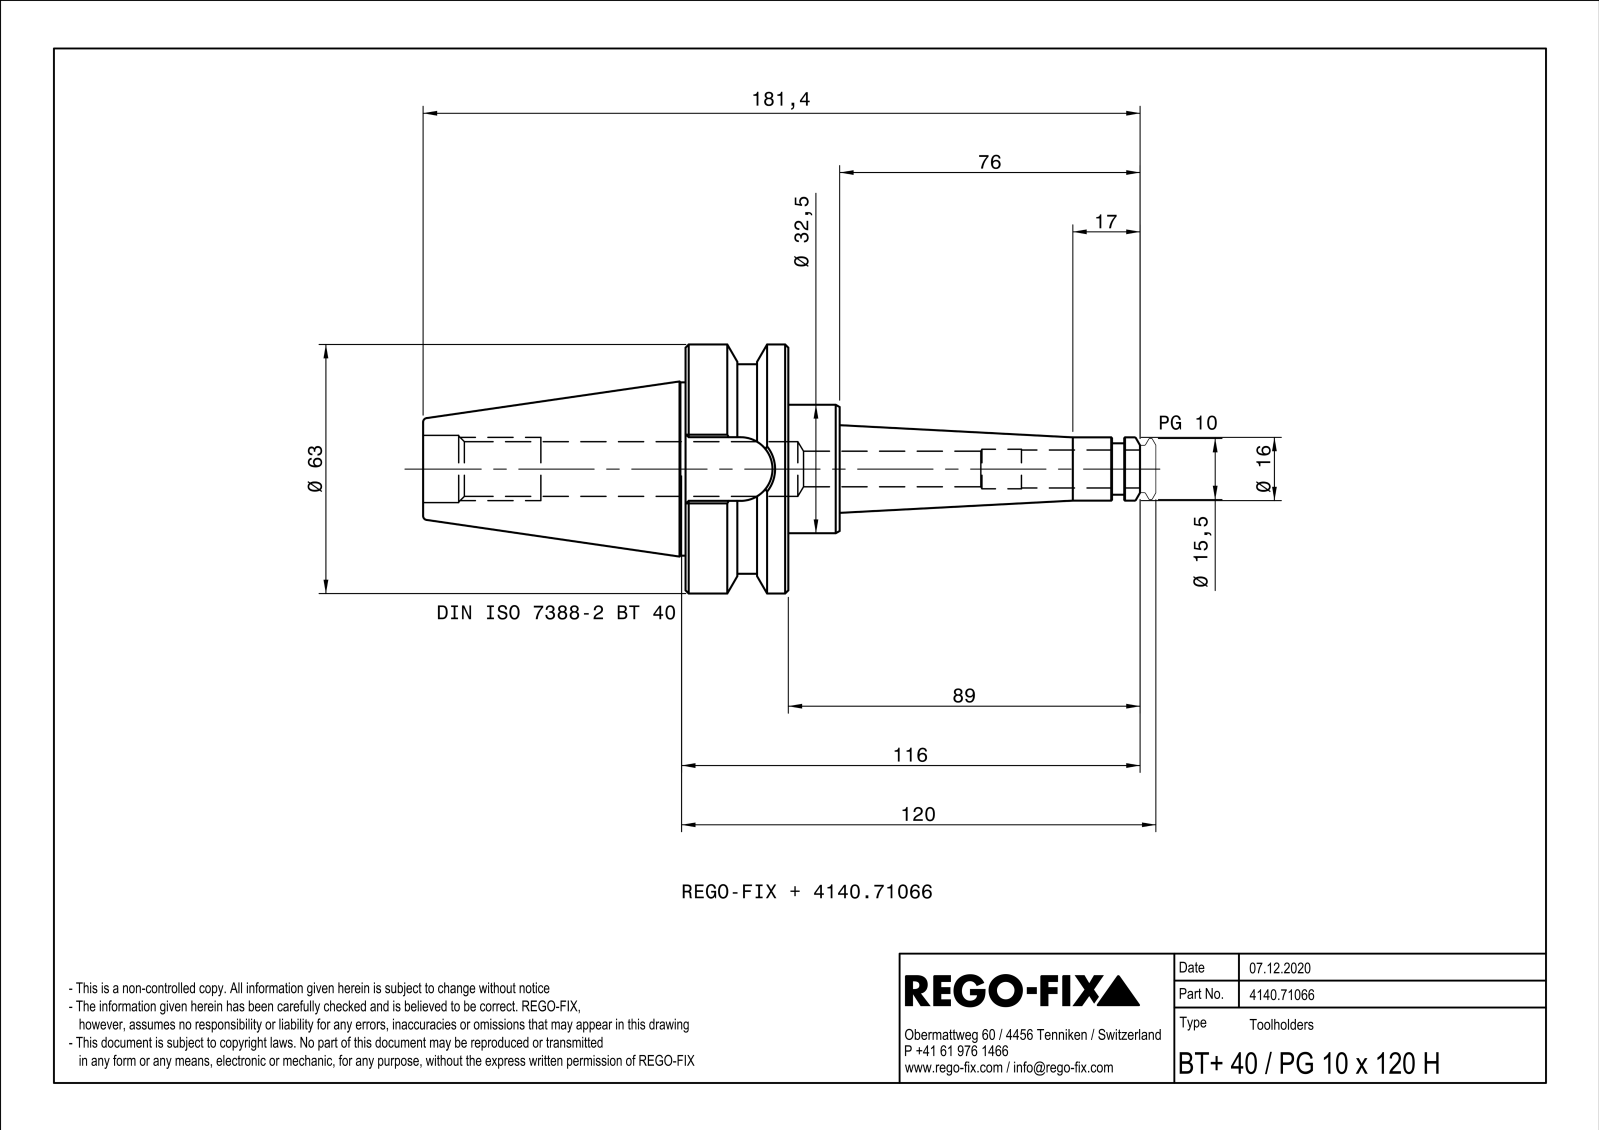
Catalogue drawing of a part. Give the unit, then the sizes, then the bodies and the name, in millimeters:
Units: millimetres
Overall size (bounding box): 181.4 × 63 × 63
Round holes (diameter × count): ⌀9 ×1, ⌀10 ×1, ⌀13.83 ×1, ⌀13.84 ×1, ⌀17 ×1
Round bosses / shafts (diameter × count): ⌀63 ×1, ⌀53 ×1, ⌀43.85 ×1, ⌀32.5 ×1, ⌀16 ×1, ⌀13 ×1
Partial cylindrical surfaces — rounded edges, fillets, slot ends (radius × count): R0.5 ×8, R8.05 ×1
Main face-to-face distances: 26, 45.1, 13, 39, 105.4, 92.4, 66.4, 16.1, 85, 3.1
Volume: 145 025 mm³ · Surface area: 30 663 mm²
Bodies: 1 solid, 105 faces (28 planar, 27 cylindrical, 50 other)
Part name (STEP PRODUCT): NOCUT
STEP written by: SIEMENS PLM Software Solid Edge ST10 (AUTOMOTIVE_DESIGN)
